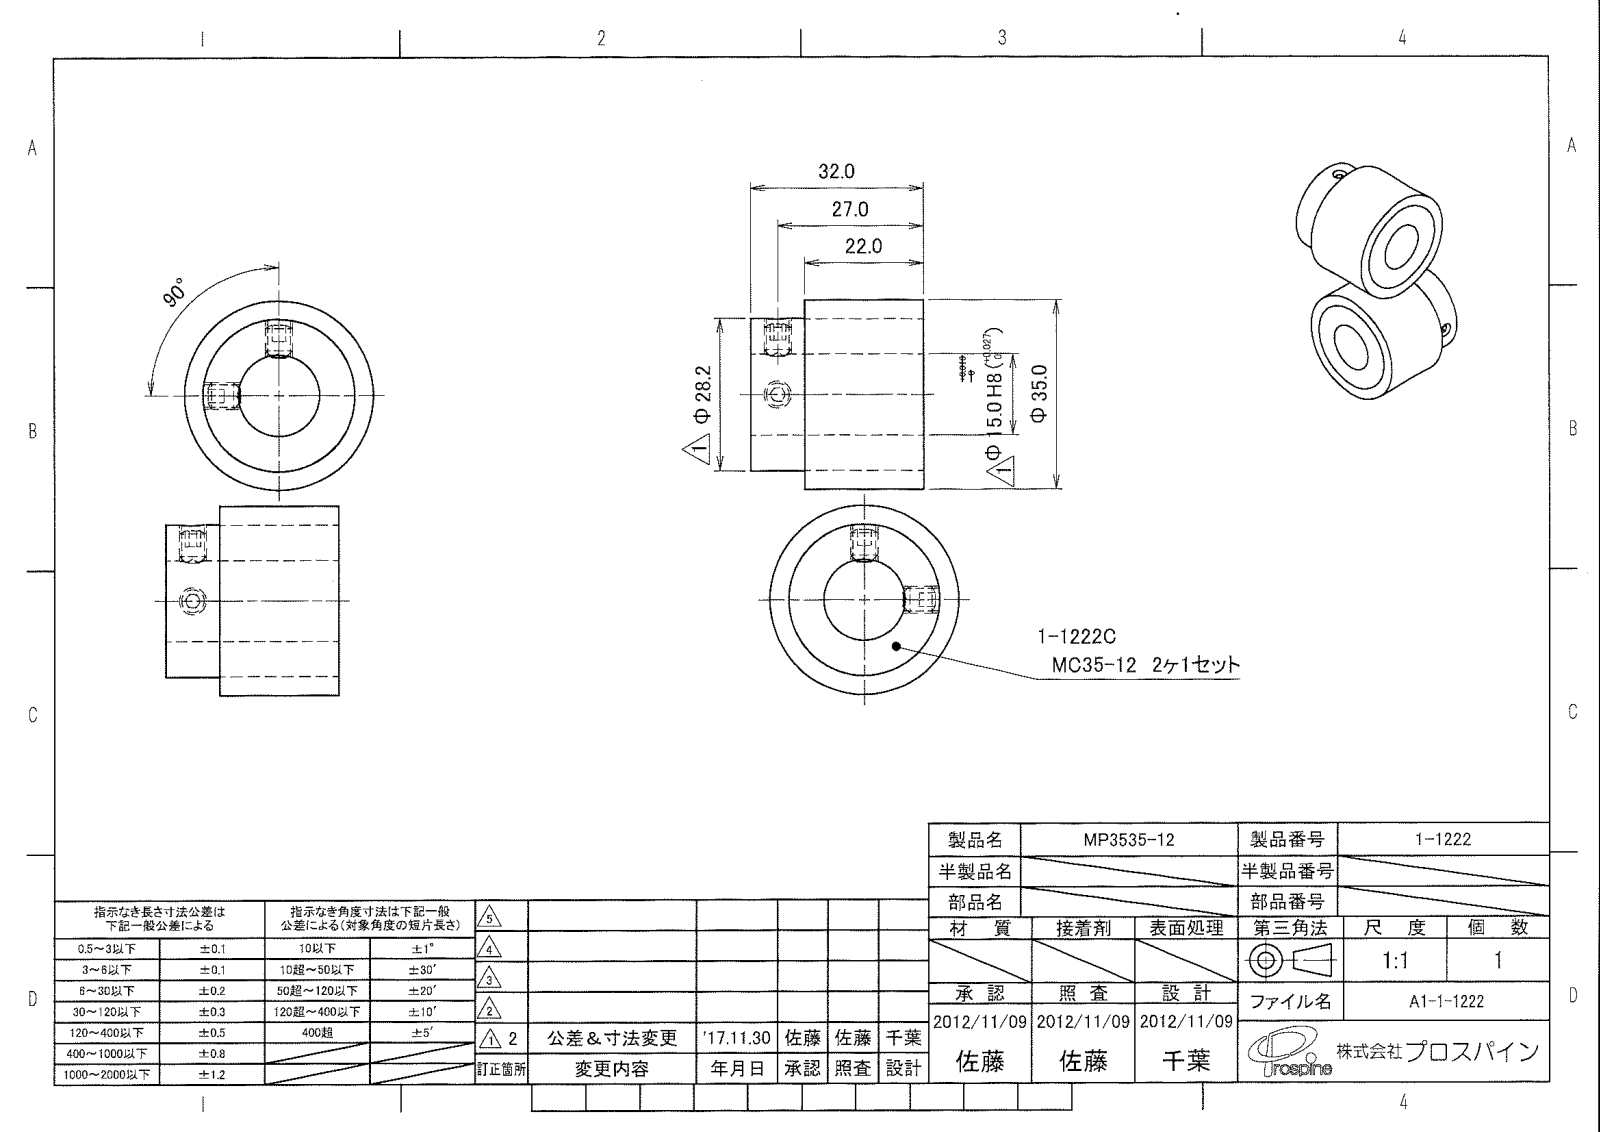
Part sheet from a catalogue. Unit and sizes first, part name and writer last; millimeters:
Units: millimetres
Overall size (bounding box): 200 × 35 × 35
Round holes (diameter × count): ⌀4.2 ×2, ⌀15 ×1, ⌀28 ×1
Round bosses / shafts (diameter × count): ⌀5 ×2, ⌀35 ×1, ⌀28.2 ×1
Main face-to-face distances: 32, 10, 22, 2.5, 11.3, 8.91, 8.8, 11.41
Volume: 21 914 mm³ · Surface area: 10 945 mm²
Bodies: 6 solids, 56 faces (33 planar, 11 cylindrical, 12 other)
STEP written by: PSStep 10.0 (CONFIG_CONTROL_DESIGN)
